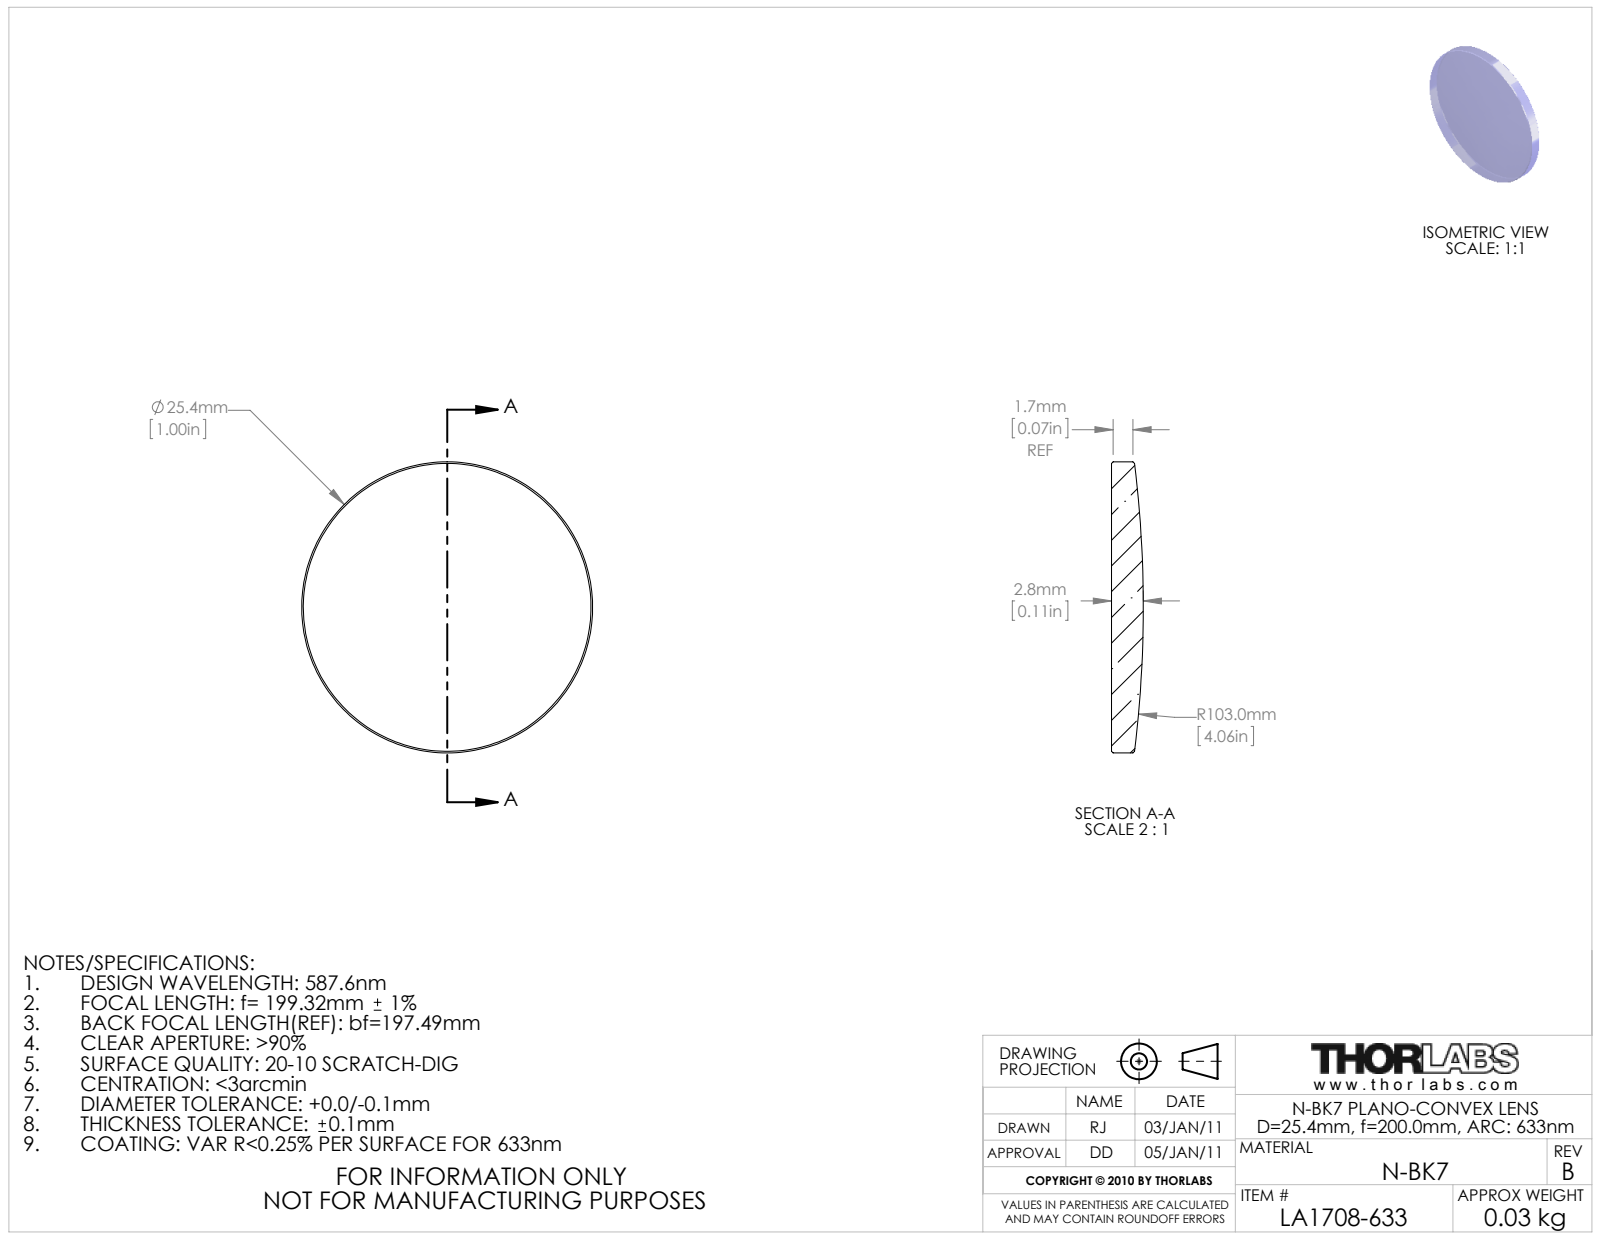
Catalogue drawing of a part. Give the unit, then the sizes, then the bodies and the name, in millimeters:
Units: millimetres
Overall size (bounding box): 25.4 × 25.4 × 2.78
Round bosses / shafts (diameter × count): ⌀25.4 ×1
Bodies: 0 solids, 9 faces (1 planar, 2 cylindrical, 6 other)
Part name (STEP PRODUCT): 21798-E0W
STEP written by: SolidWorks 2011 (AUTOMOTIVE_DESIGN)
